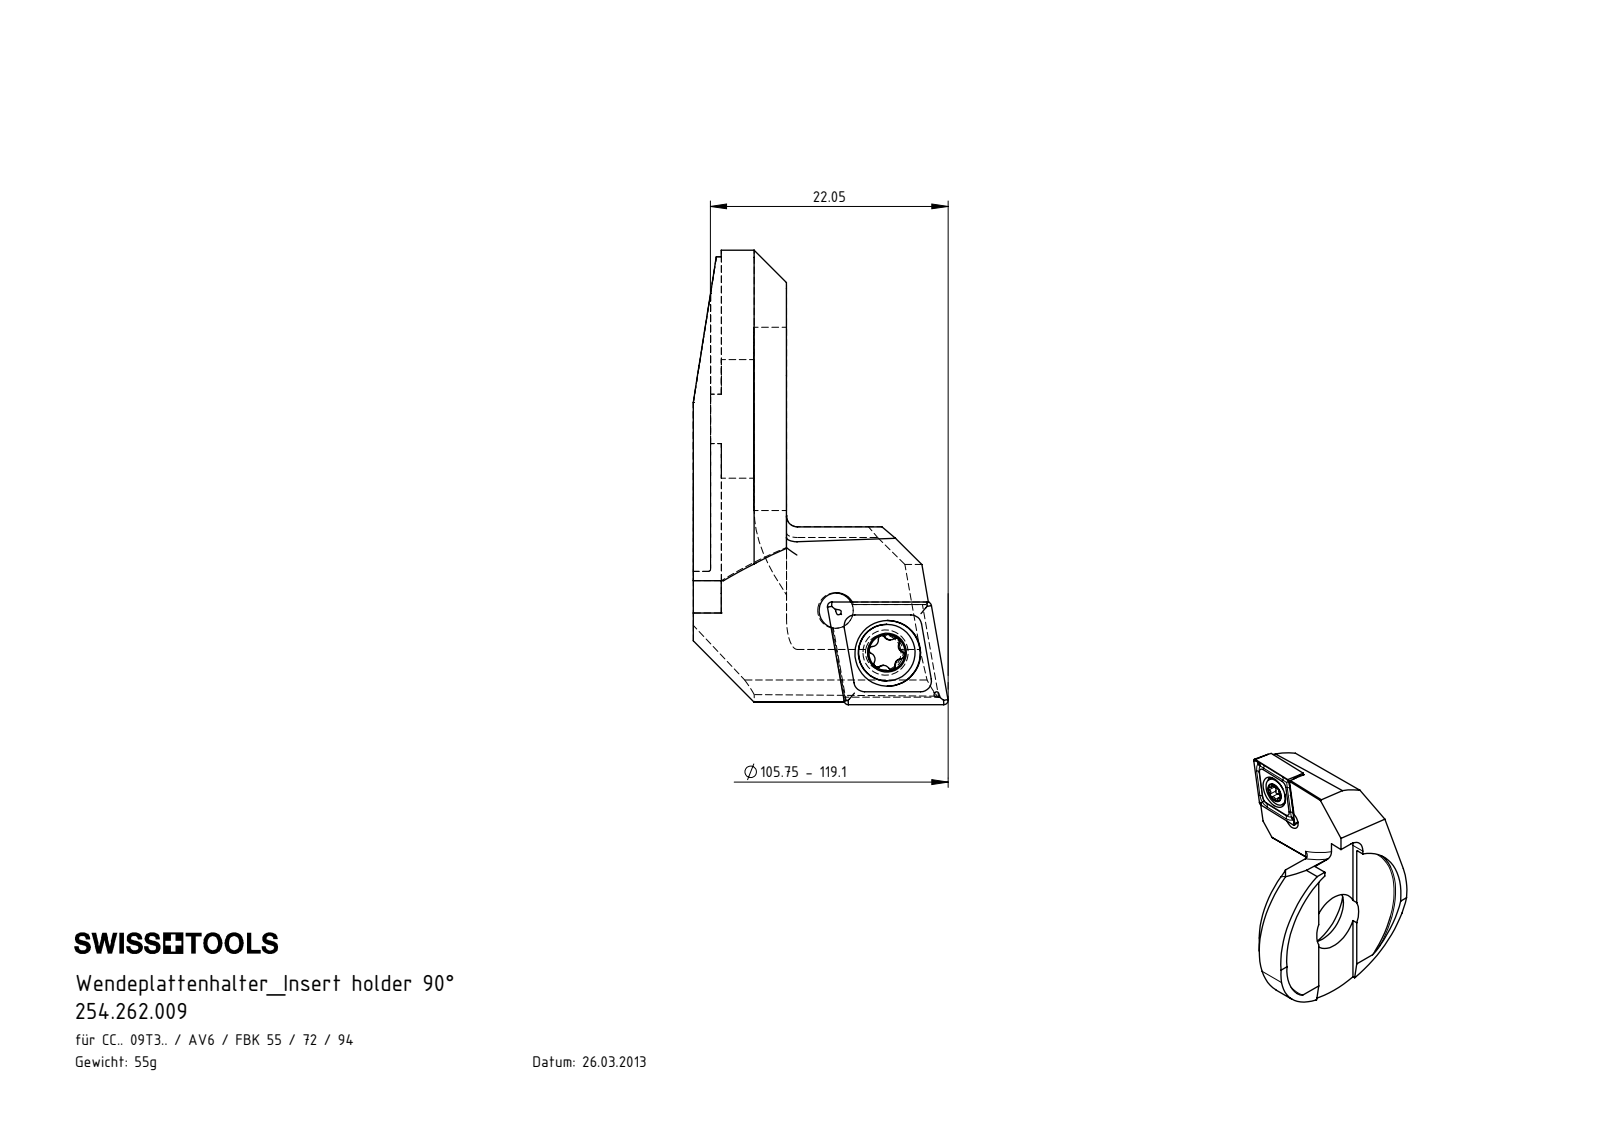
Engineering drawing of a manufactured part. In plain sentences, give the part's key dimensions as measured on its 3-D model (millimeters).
The part is named "AV6-WCB.001.022_A_fertigbearbeitet; 254.262.009; WCB-ER2.001.009_A; CCMT09T304". Its 3-D file was written by "SolidWorks 2017 (CONFIG_CONTROL_DESIGN)". It is 3 solids with 163 faces: 52 planar, 51 cylindrical and 60 other. Overall it measures 42.15 by 33.1 by 23.65 millimeters. Its volume is 7 068 cubic millimeters and its surface area 4 025 square millimeters. Round holes: 2 of diameter 3.3, 1 of diameter 4.4, 1 of diameter 6.1, 1 of diameter 11, 1 of diameter 17. Round bosses or shafts: 1 of diameter 5.25, 1 of diameter 4. Partial cylindrical surfaces (rounded edges, fillets, slot ends): 6 of radius 0.34, 6 of radius 0.59, 6 of radius 1, 3 of radius 15, 2 of radius 3.2, 1 of radius 16.55, 1 of radius 20.95, 1 of radius 40. The main face-to-face distances are 7.05, 1, 6.05, 3, 3.05, 4, 8.65, 5.6, 2.6, 1.6. The hole center spacings are 6.06, 6.17.
